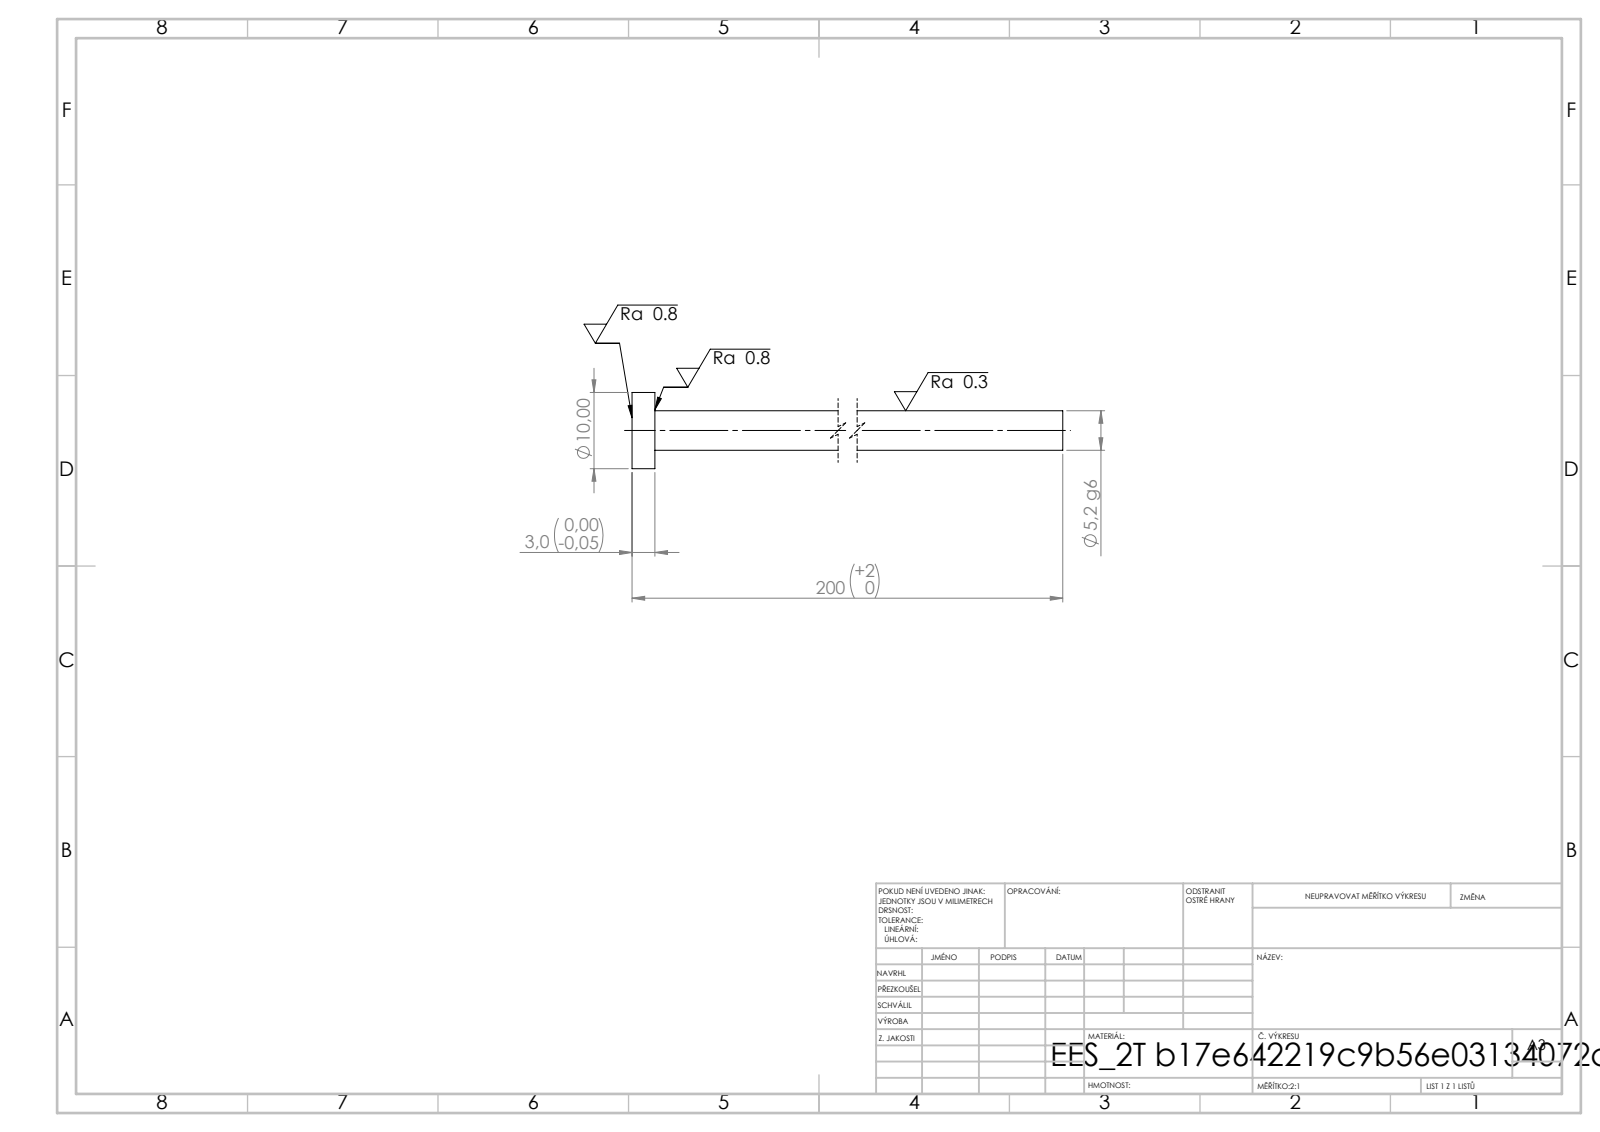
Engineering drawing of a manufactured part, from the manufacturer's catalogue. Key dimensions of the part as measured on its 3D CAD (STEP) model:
STEP written by: SolidWorks 2019 (CONFIG_CONTROL_DESIGN)
Units: millimetres
Bodies: 1 solid, 7 faces (3 planar, 4 cylindrical, 0 other)
Overall size (bounding box): 200 × 10 × 10
Volume: 4 419 mm³ · Surface area: 3 470 mm²
Round bosses / shafts (diameter × count): ⌀10 ×1, ⌀5.2 ×1
Main face-to-face distances: 3, 200, 197
